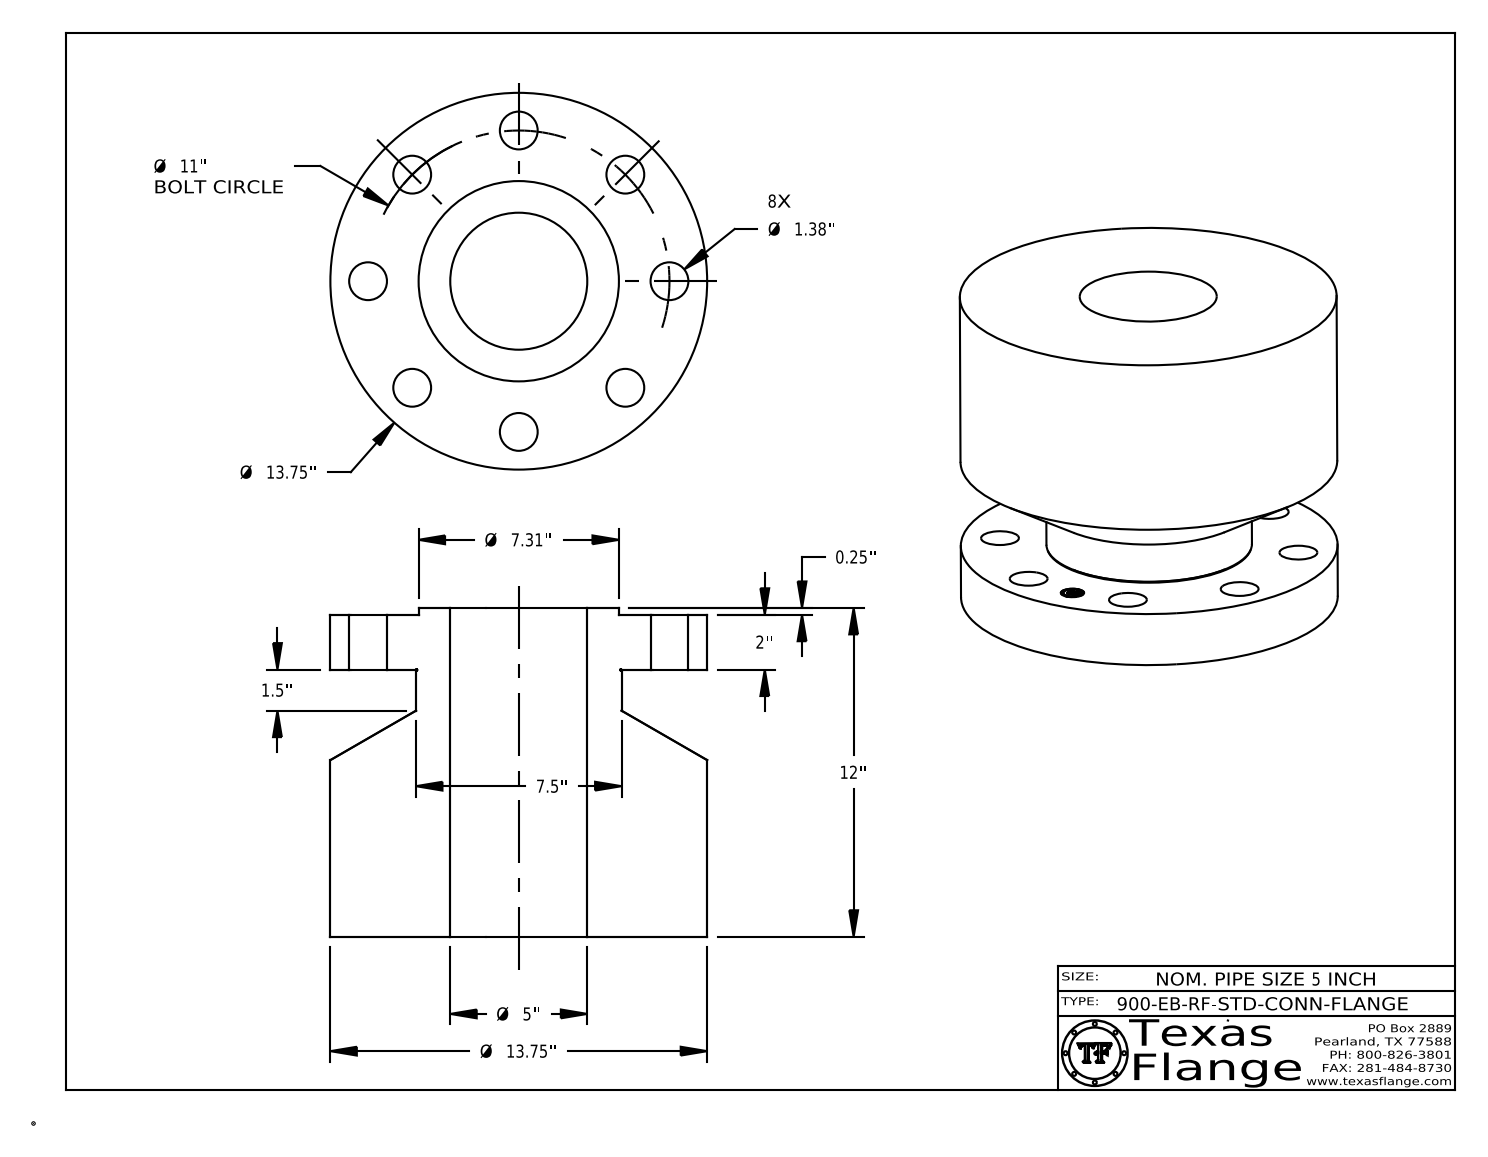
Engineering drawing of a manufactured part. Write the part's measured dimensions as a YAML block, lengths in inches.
part_name: "5-900-EB-RF-STD-CONN-FLANGE"
step_written_by: "CATIA V5 STEP AP214 (AUTOMOTIVE_DESIGN)"
units: inches
bodies: {solids: 1, faces: 421, planar: 369, cylindrical: 46, other: 6}
overall_size: [13.75, 13.75, 12]
volume: 1236
surface_area: 1123
round_holes:
  - {diameter: 1.38, count: 8}
  - {diameter: 0.85, count: 1}
  - {diameter: 5, count: 1}
round_bosses_or_shafts:
  - {diameter: 0.051, count: 8}
  - {diameter: 13.75, count: 1}
  - {diameter: 7.5, count: 1}
  - {diameter: 7.31, count: 1}
  - {diameter: 0.67, count: 1}
face_to_face_distances: [11.75, 2, 9.75, 0.25, 2.25, 12, 2.245, 1.995, 9.755, 0.254]
hole_center_spacings: [5.5, 4.209, 10.163, 7.778, 7.778, 2.146, 9.146, 11]
